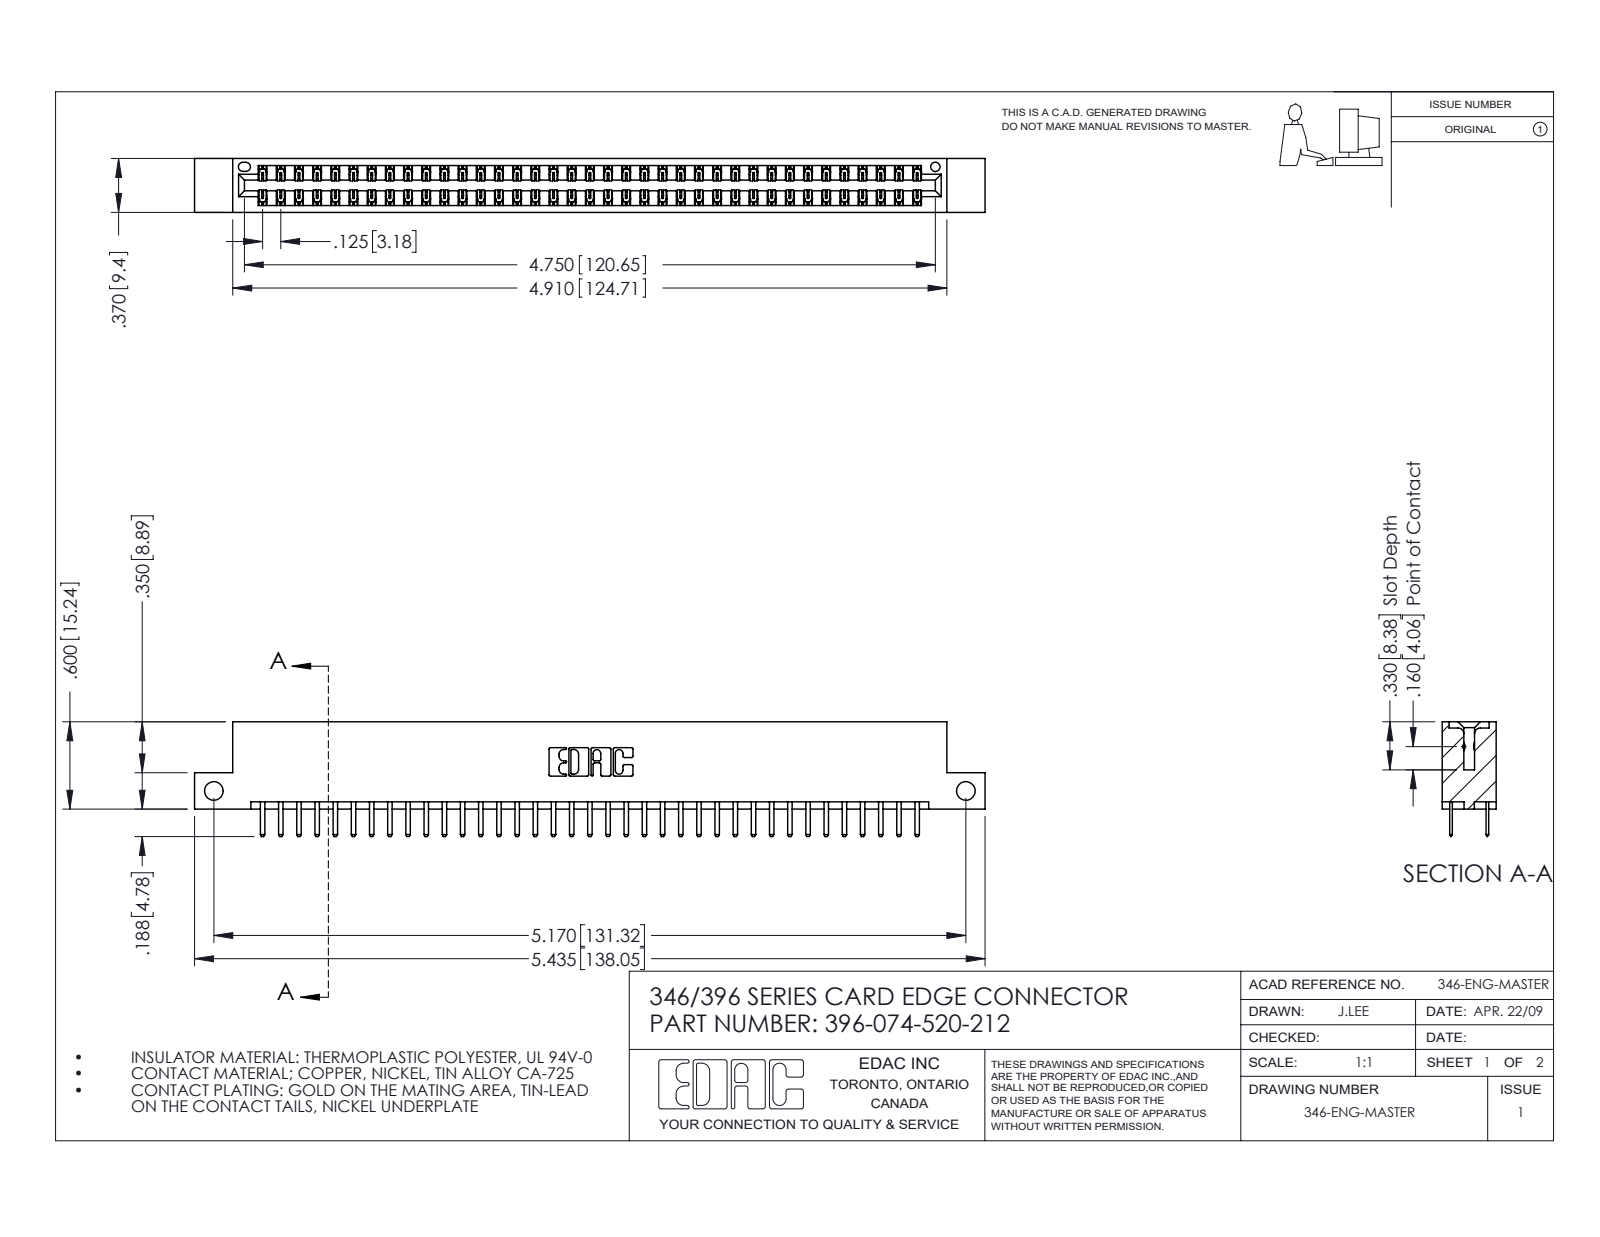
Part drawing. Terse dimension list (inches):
name: 346 Part_Flush Mounting Lugs - Side Mount; 396-074-520-212; 345-292-001_345-293-120
written by: SolidWorks 2016 (CONFIG_CONTROL_DESIGN)
unit: in
bodies: 75 solids, 4266 faces (2814 planar, 1452 cylindrical, 0 other)
size: 5.435 × 0.788 × 0.37
volume: 0.812 in³; area: 27.89 in²
holes: 2× ⌀0.128, 1× ⌀0.064
rounds: 111× R0.006, 78× R0.01, 22× R0.01, 6× R0.007, 6× R0.031, 3× R0.026, 2× R0.014, 2× R0.022
face distances: 0.048, 0.322, 0.25, 0.37, 0.275, 0.072, 0.298, 0.025, 0.148, 0.222
hole spacings: 5.17
